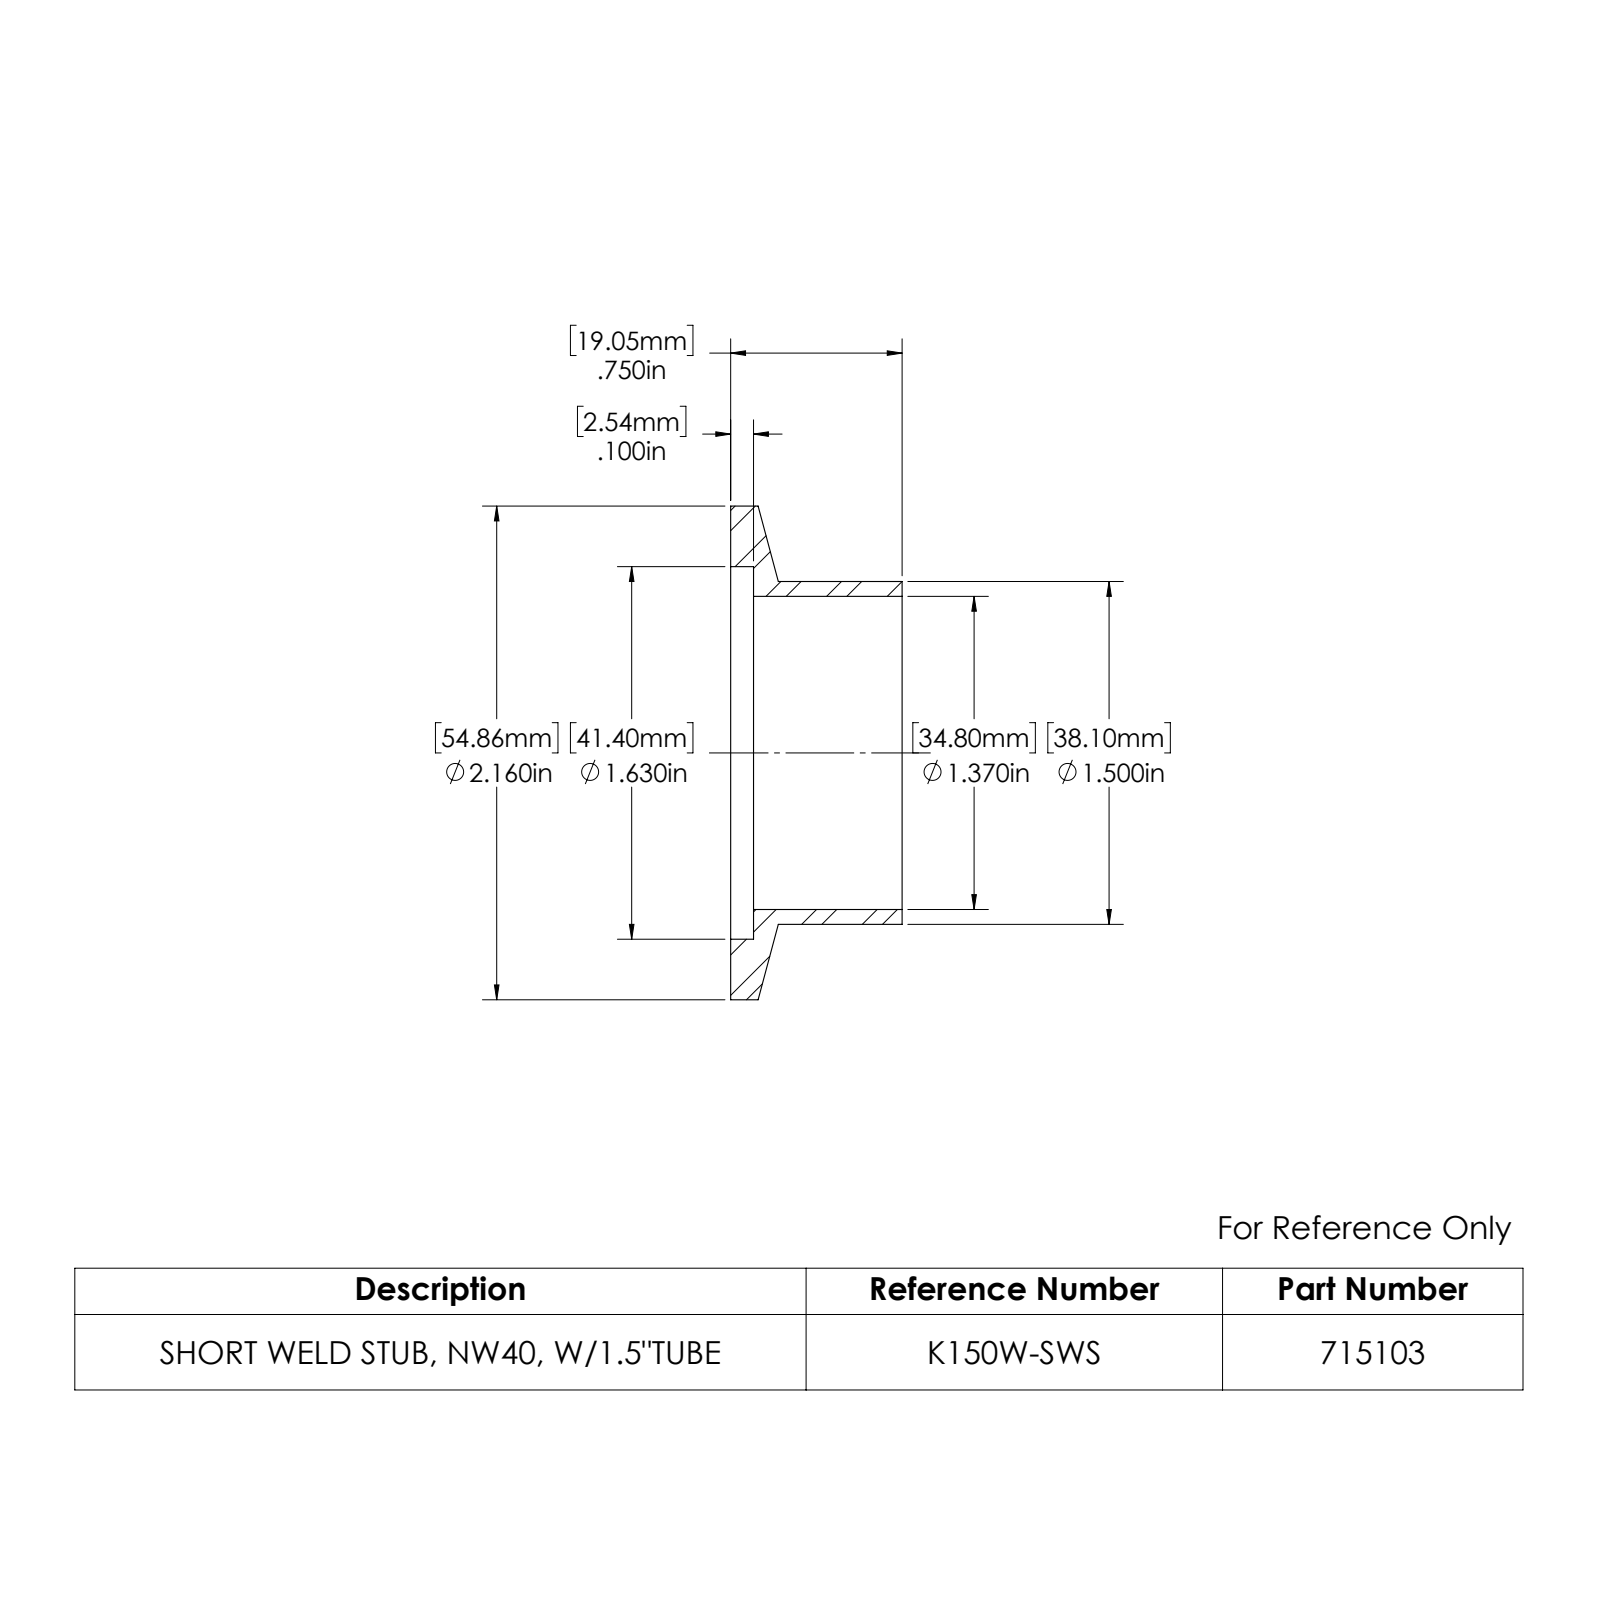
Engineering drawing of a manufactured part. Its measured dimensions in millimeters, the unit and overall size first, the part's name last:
Units: millimetres
Overall size (bounding box): 54.9 × 54.9 × 19.1
Round holes (diameter × count): ⌀34.8 ×1, ⌀41.4 ×1
Round bosses / shafts (diameter × count): ⌀54.9 ×1, ⌀38.1 ×1
Main face-to-face distances: 2.5, 16.5, 19.1
Volume: 7 620 mm³ · Surface area: 7 174 mm²
Bodies: 1 solid, 13 faces (3 planar, 8 cylindrical, 2 other)
Part name (STEP PRODUCT): 715103
STEP written by: SolidWorks 2022 (AUTOMOTIVE_DESIGN)
